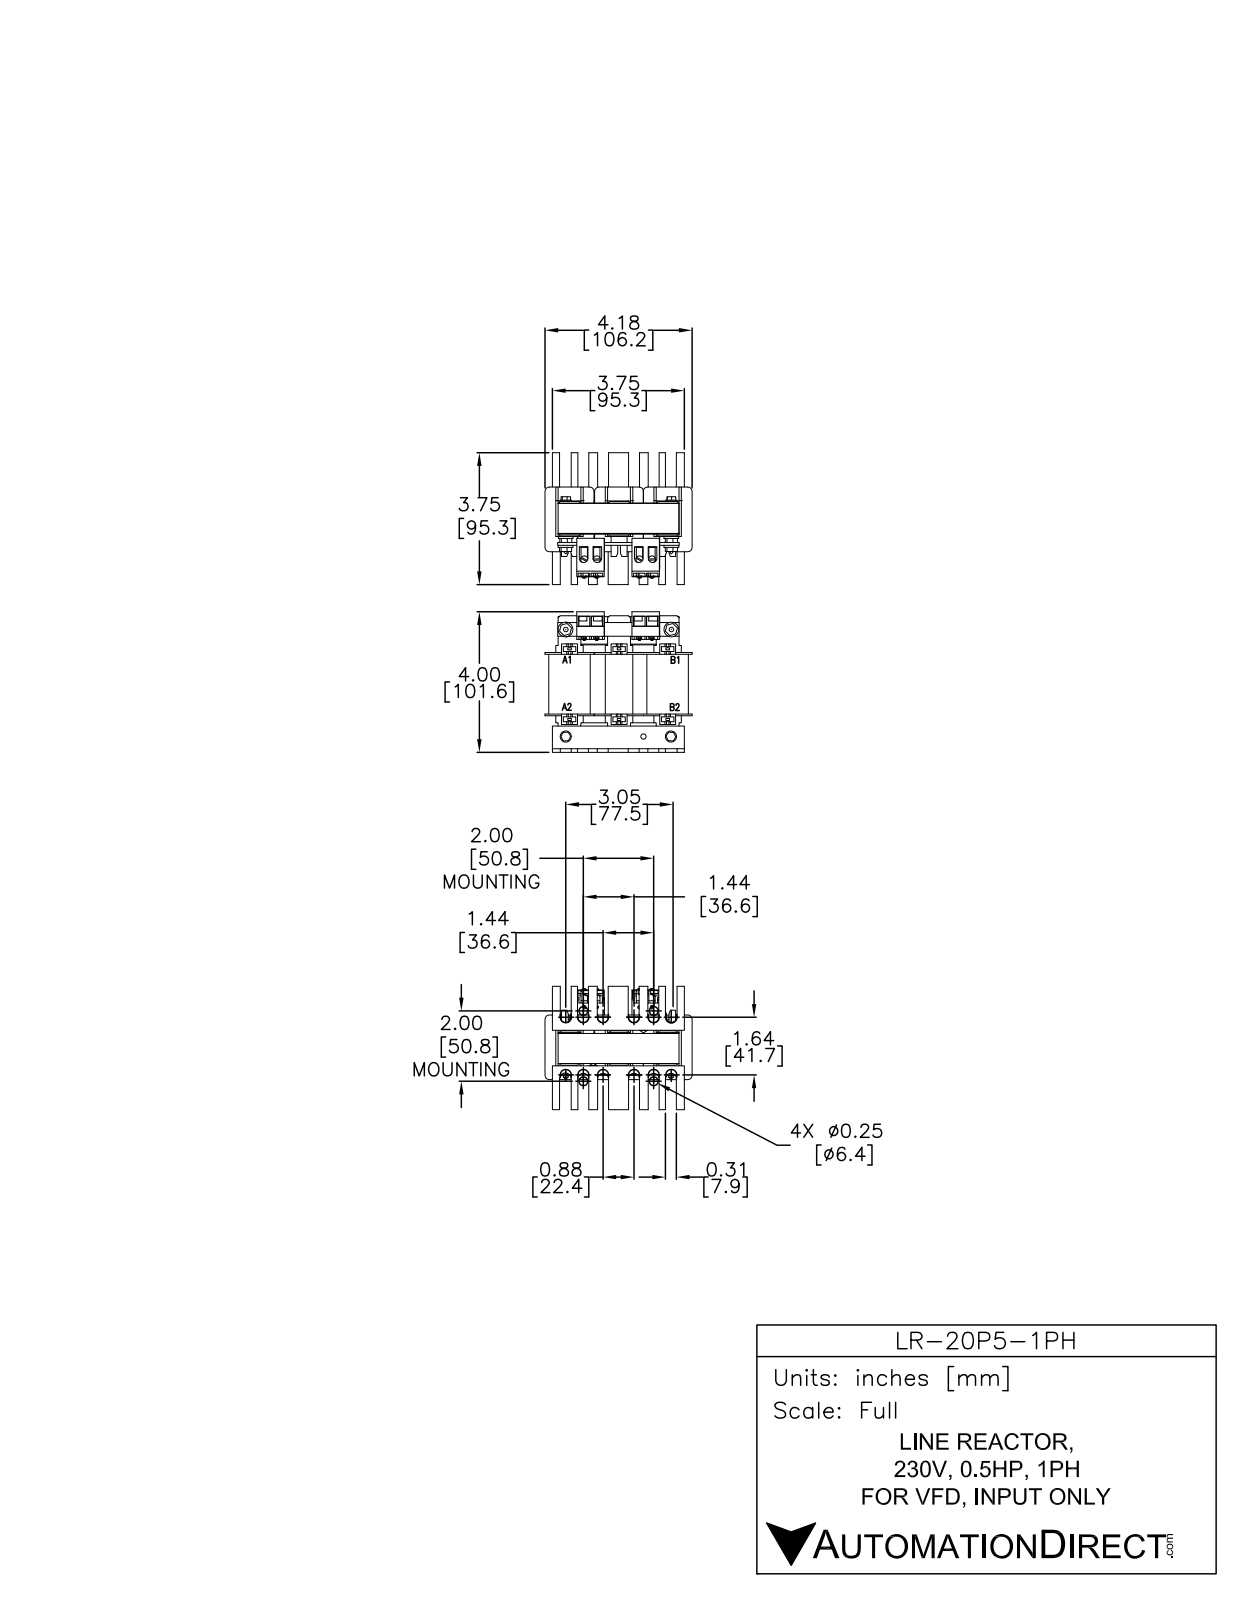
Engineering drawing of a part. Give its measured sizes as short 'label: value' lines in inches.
name: LR-20P5-1PH
written by: SolidWorks 2011 (AUTOMOTIVE_DESIGN)
unit: in
bodies: 17 solids, 1066 faces (846 planar, 220 cylindrical, 0 other)
size: 4.144 × 3.874 × 3.514
volume: 17.72 in³; area: 168.2 in²
bosses: 4× ⌀0.305, 4× ⌀0.138
rounds: 42× R0.157, 24× R0.072, 12× R0.315, 8× R0.039, 4× R0.118, 3× R0.034, 2× R0.049
face distances: 0.197, 1.033, 0.098, 0.295, 2.008, 1.909, 1.713, 0.108, 0.846, 1.142
